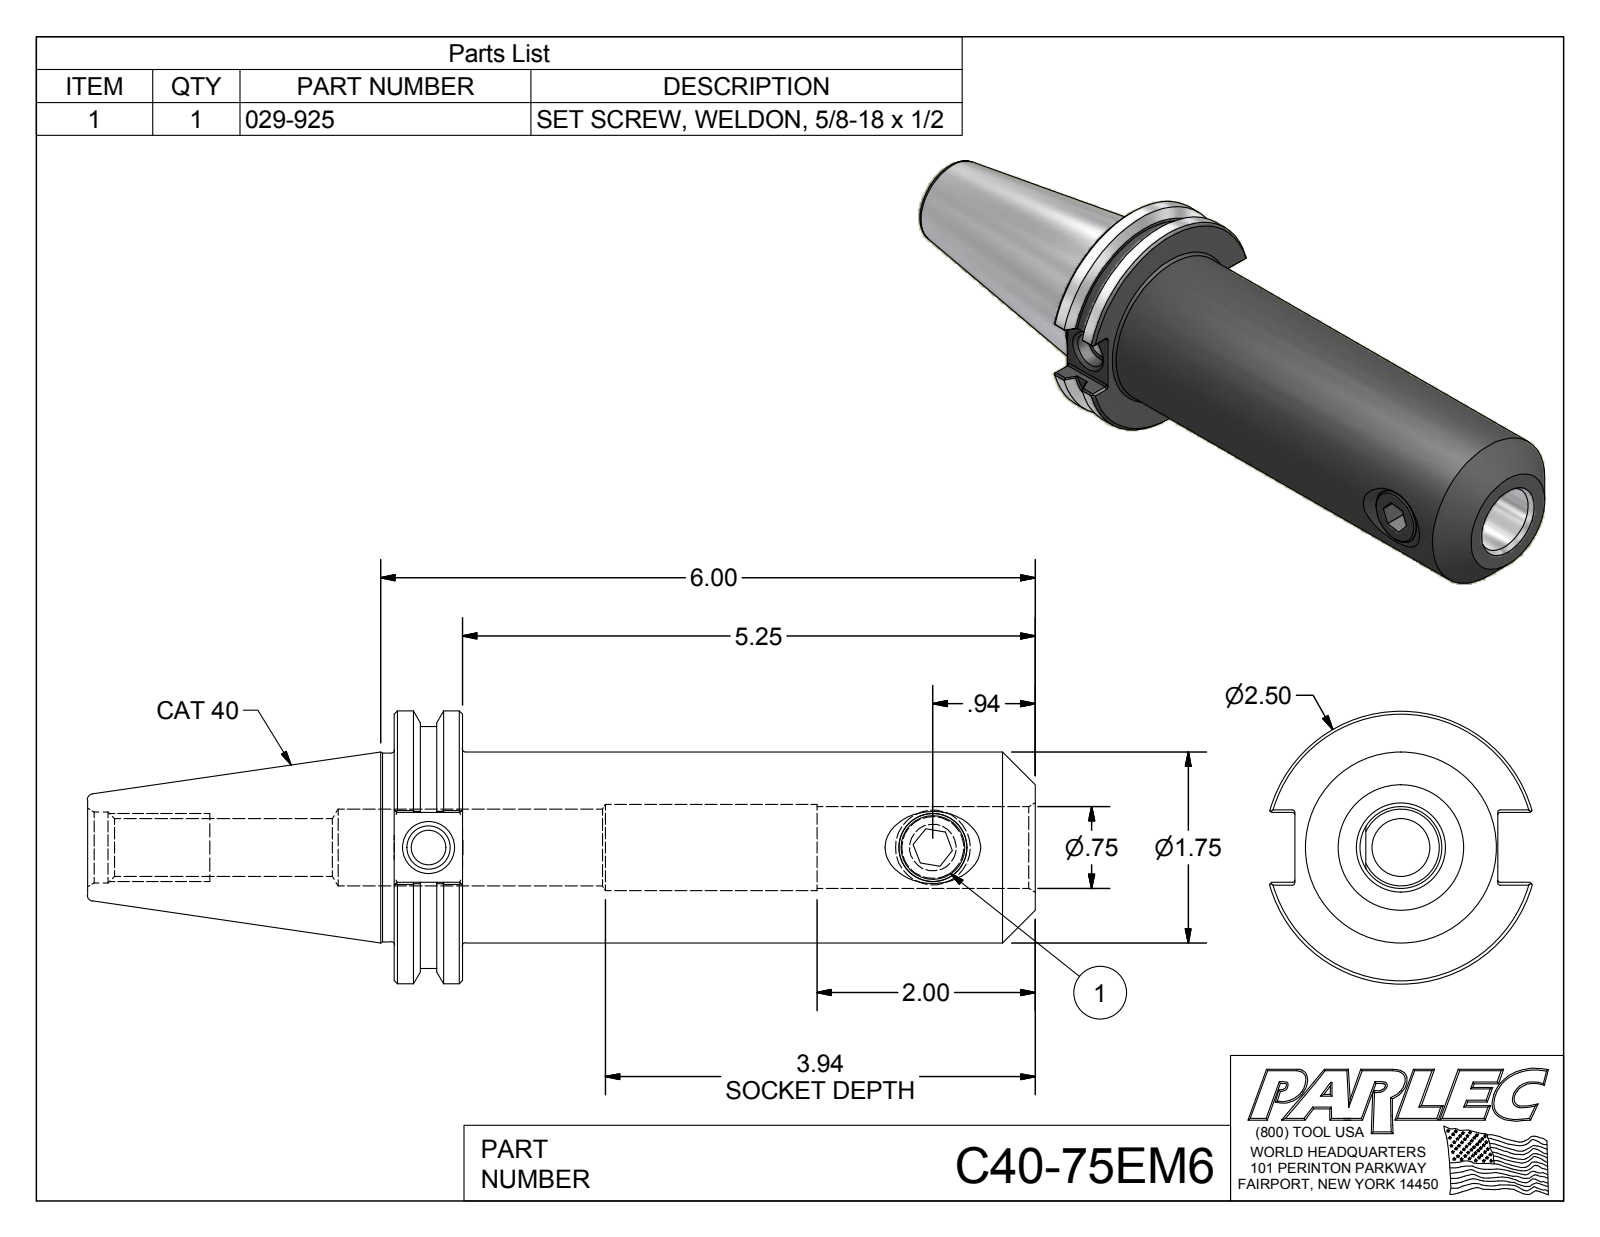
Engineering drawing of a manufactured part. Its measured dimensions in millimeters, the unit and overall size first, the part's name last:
Units: millimetres
Overall size (bounding box): 220.6 × 63.5 × 61.1
Round holes (diameter × count): ⌀8 ×1, ⌀10.1 ×1, ⌀13.4 ×1, ⌀15.9 ×1, ⌀16.5 ×1, ⌀17.9 ×1, ⌀19.1 ×1, ⌀20.1 ×1
Round bosses / shafts (diameter × count): ⌀63.5 ×1, ⌀56.4 ×1, ⌀44.5 ×1, ⌀43.9 ×1
Partial cylindrical surfaces — rounded edges, fillets, slot ends (radius × count): R0.5 ×12, R11.1 ×1
Main face-to-face distances: 15.9, 149.2, 133.4, 16.3, 8, 47.2, 71.4, 87.3, 220.6, 43.4
Hole centre spacings: 117.4
Volume: 261 000 mm³ · Surface area: 47 880 mm²
Bodies: 2 solids, 104 faces (41 planar, 31 cylindrical, 32 other)
Part name (STEP PRODUCT): C40-75EM6; C40-75EM6-1; 029-925
STEP written by: Autodesk Inventor 2012 (AUTOMOTIVE_DESIGN)
